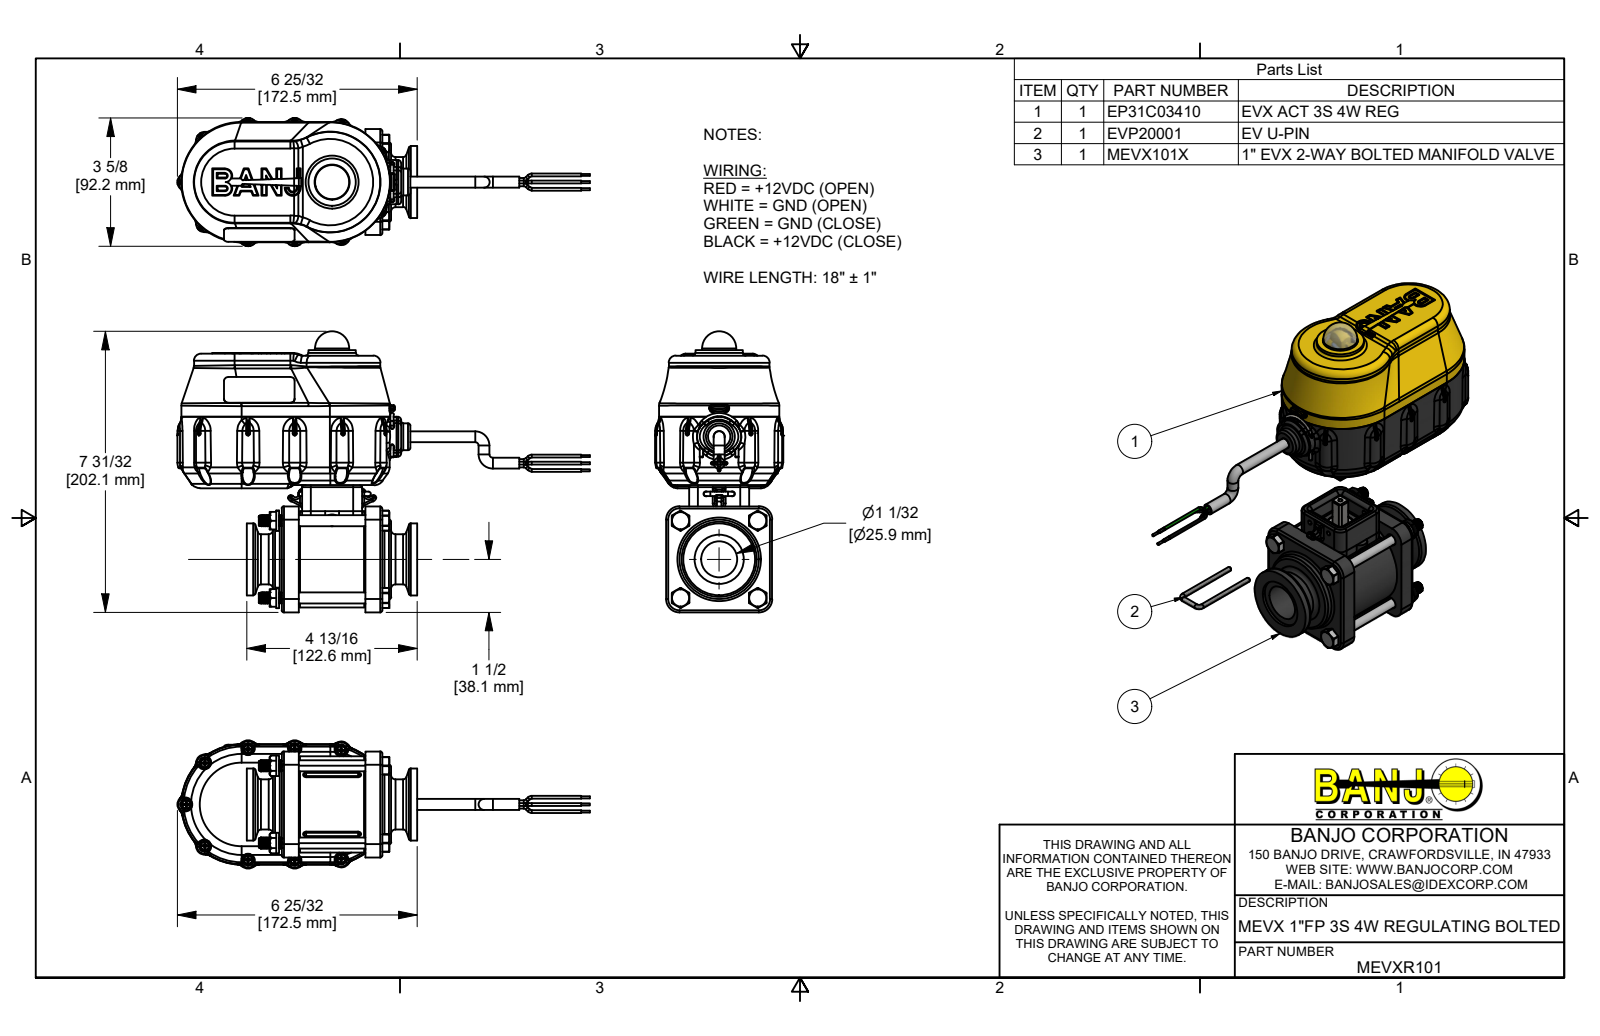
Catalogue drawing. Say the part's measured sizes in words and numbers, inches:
The part is named "MEVXR101; EP31C03410; 91400A119; 95584A200 (+8 more)". Its 3-D file was written by "Autodesk Inventor 2021 (AUTOMOTIVE_DESIGN)". It is 95 solids with 12757 faces: 3546 planar, 3485 cylindrical and 5726 other. Overall it measures 11.685 by 7.957 by 3.63 inches. Its volume is 51.06 cubic inches and its surface area 584.4 square inches. Round holes: 13 of diameter 0.15, 11 of diameter 0.095, 4 of diameter 0.107, 4 of diameter 0.126, 4 of diameter 0.136, 4 of diameter 0.17, 4 of diameter 0.252, 4 of diameter 0.322, 4 of diameter 0.36, 3 of diameter 0.135, 3 of diameter 1.02, 2 of diameter 0.089. Round bosses or shafts: 60 of diameter 0.268, 20 of diameter 0.08, 17 of diameter 0.25, 11 of diameter 0.14, 11 of diameter 0.108, 11 of diameter 0.085, 8 of diameter 0.058, 5 of diameter 0.313. Partial cylindrical surfaces (rounded edges, fillets, slot ends): 147 of radius 0.04, 109 of radius 0.02, 52 of radius 0.01, 46 of radius 0.06, 45 of radius 0.03, 41 of radius 0.005, 31 of radius 0.015, 28 of radius 0.08. The main face-to-face distances are 0.1, 2.565, 1.685, 0.78, 2.465, 0.055, 0.48, 0.165, 0.88, 0.035. The hole center spacings are 1.283, 1.547, 2.188, 1.662, 1.891, 2.73, 2.967, 3.294.
